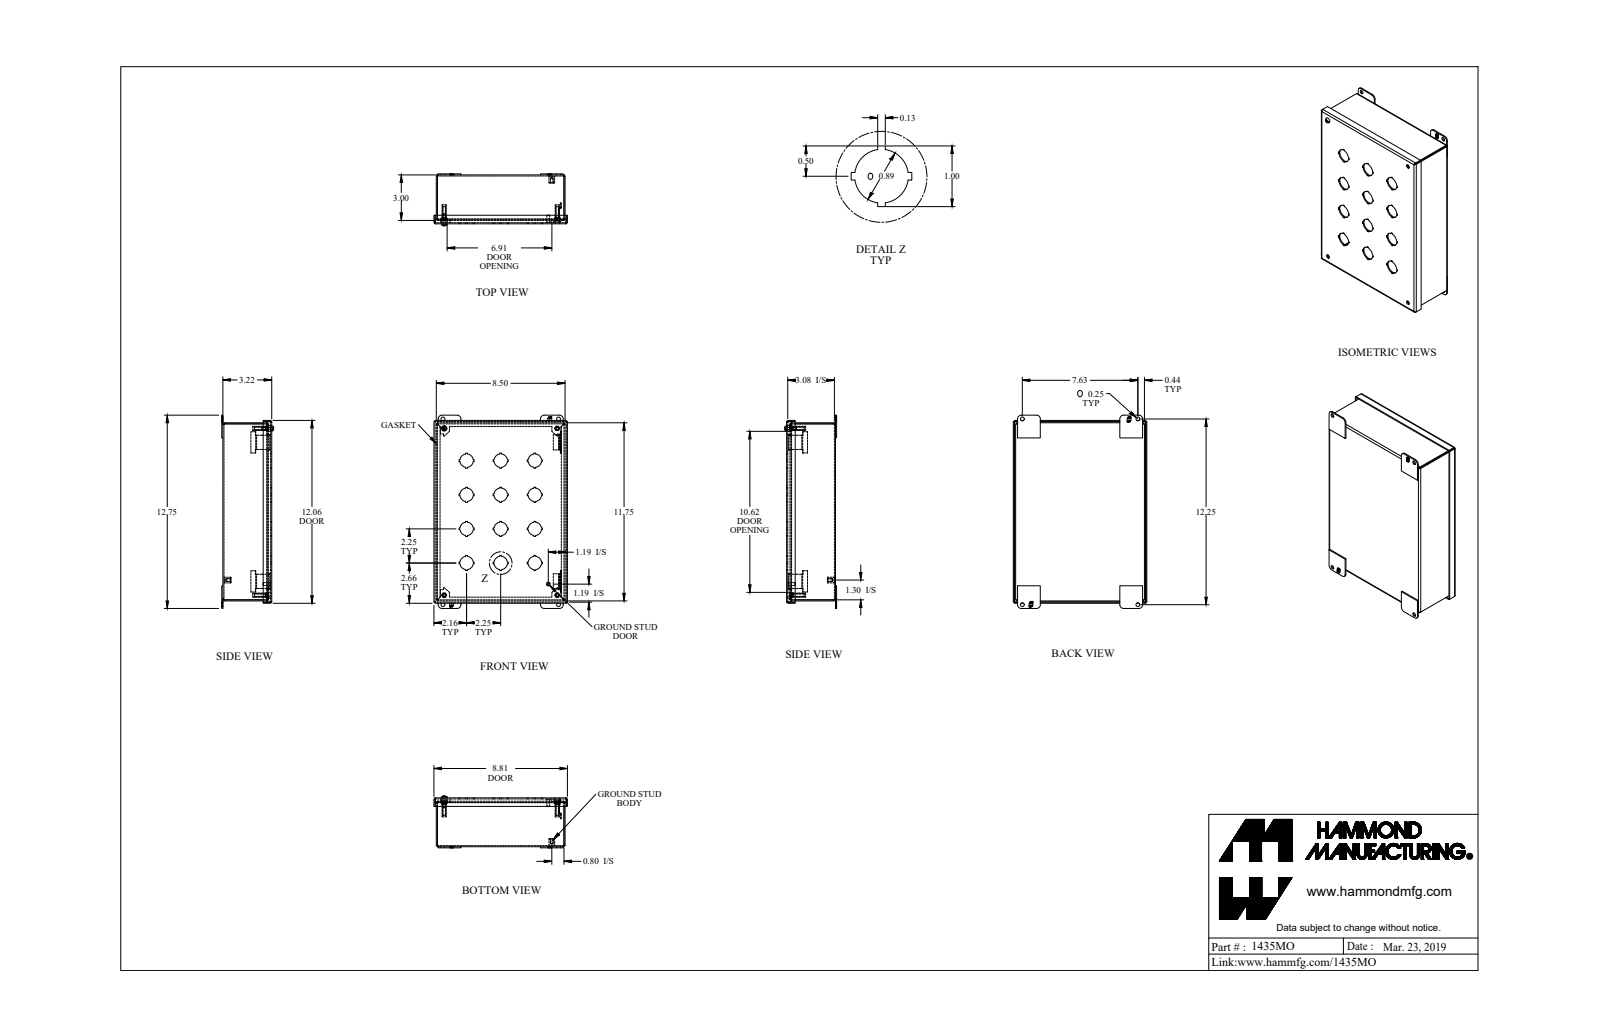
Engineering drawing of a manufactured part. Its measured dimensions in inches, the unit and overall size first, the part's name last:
Units: inches
Overall size (bounding box): 12.75 × 8.812 × 3.421
Round holes (diameter × count): ⌀0.886 ×12, ⌀0.25 ×8, ⌀0.159 ×4, ⌀0.406 ×4, ⌀0.156 ×1
Round bosses / shafts (diameter × count): ⌀0.39 ×4, ⌀0.275 ×4, ⌀0.375 ×1, ⌀0.25 ×1, ⌀0.19 ×1, ⌀0.188 ×1, ⌀0.148 ×1
Partial cylindrical surfaces — rounded edges, fillets, slot ends (radius × count): R0.036 ×12, R0.108 ×12, R0.25 ×8, R0.029 ×4, R0.086 ×4, R0.16 ×4, R0.171 ×1
Main face-to-face distances: 0.072, 3.15, 3.222, 3.078, 8.428, 0.072, 11.678, 8.356, 8.5, 0.156
Hole centre spacings: 2.25, 5.031, 3.182, 4.5, 11, 11.626, 4.619, 0.63
Volume: 29.37 in³ · Surface area: 778.6 in²
Bodies: 17 solids, 805 faces (577 planar, 184 cylindrical, 44 other)
Part name (STEP PRODUCT): 1435MO_Default
STEP written by: SolidWorks 2019 (CONFIG_CONTROL_DESIGN)
